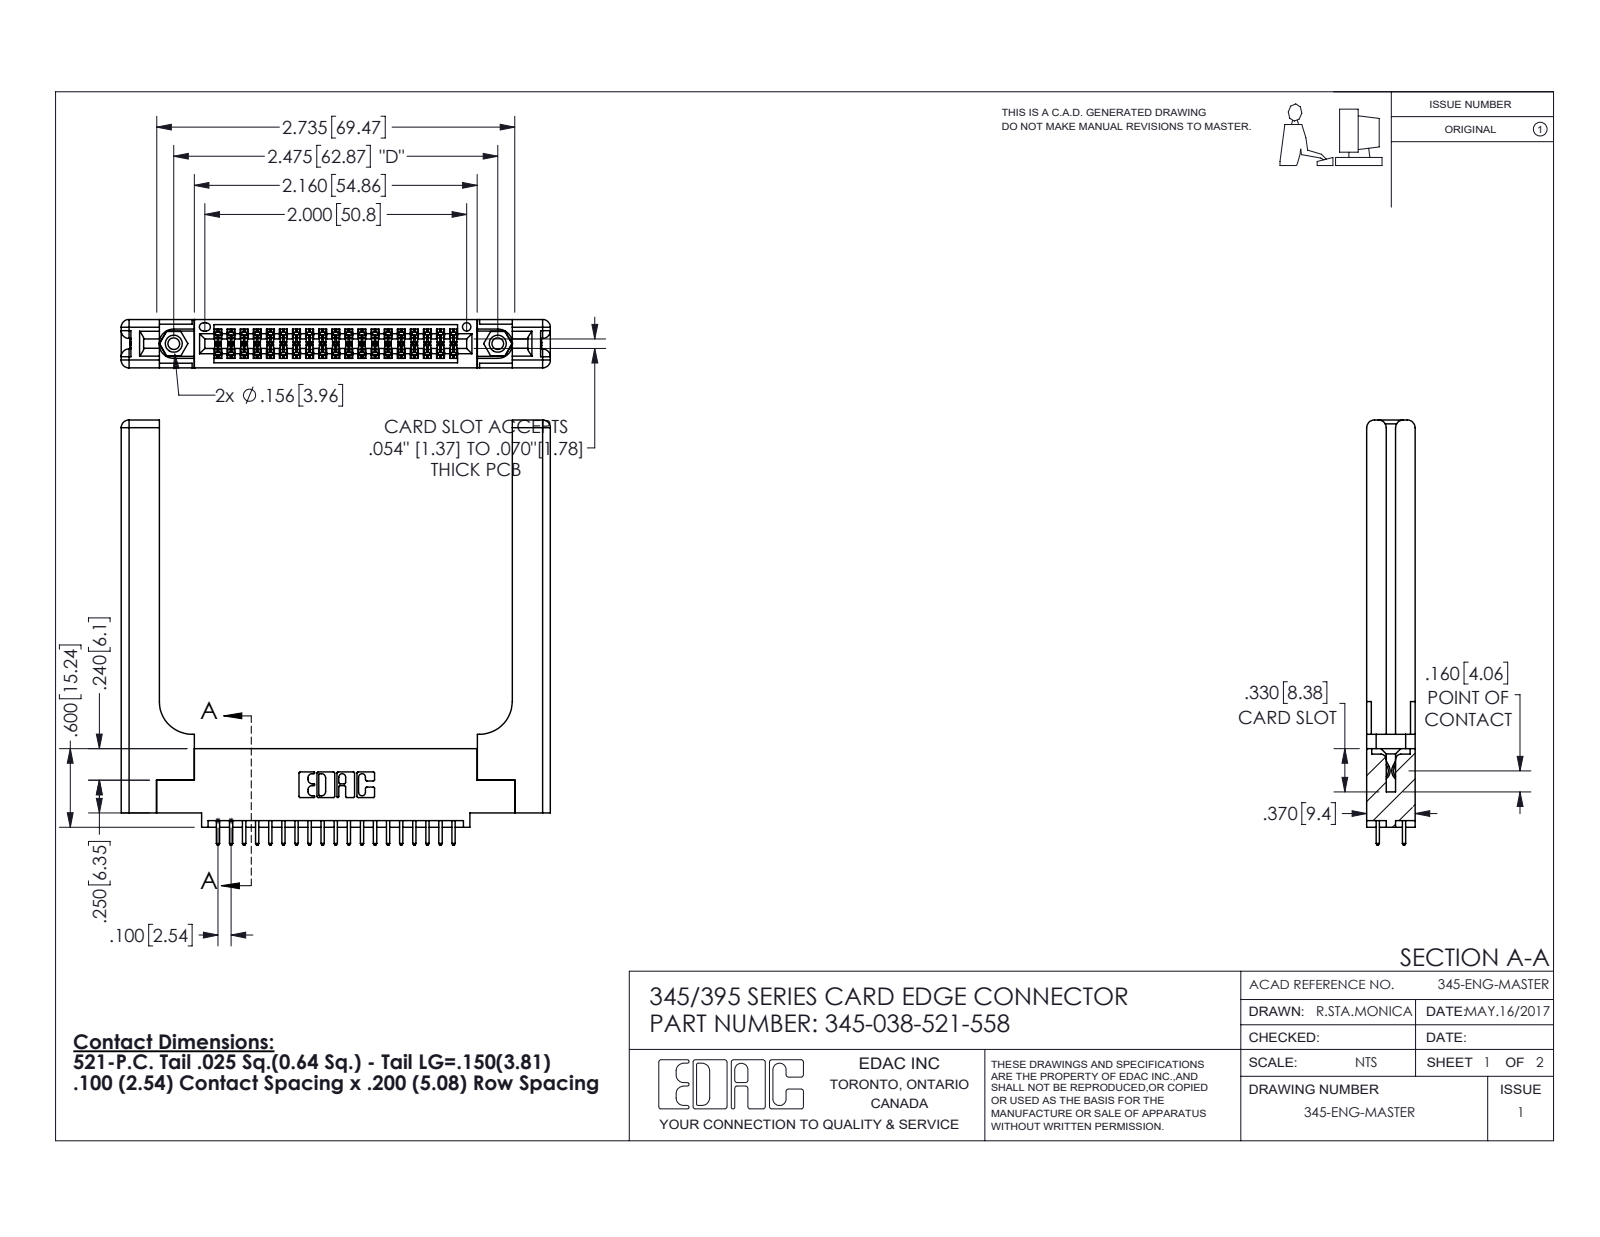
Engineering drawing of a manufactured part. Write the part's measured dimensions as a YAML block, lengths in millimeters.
part_name: "345-038-521-558; 345-250-001_345-250-001-102; 345-292-001_345-293-121; 345 Part_0.110 Offset - 0.156 Dia-TH (+1 more)"
step_written_by: "SolidWorks 2016 (CONFIG_CONTROL_DESIGN)"
units: millimeters
bodies: {solids: 43, faces: 2286, planar: 1486, cylindrical: 740, other: 60}
overall_size: [83.3, 82.5, 9.4]
volume: 16300
surface_area: 16120
round_holes:
  - {diameter: 2.3, count: 2}
  - {diameter: 3.2, count: 2}
  - {diameter: 4, count: 2}
  - {diameter: 1.6, count: 1}
round_bosses_or_shafts:
  - {diameter: 3.9, count: 2}
partial_cylinders:
  - {radius: 0.2, count: 57}
  - {radius: 0.3, count: 38}
  - {radius: 0.3, count: 22}
  - {radius: 1.5, count: 16}
  - {radius: 0.2, count: 6}
  - {radius: 0.8, count: 6}
  - {radius: 0.7, count: 3}
  - {radius: 0.4, count: 2}
face_to_face_distances: [9.4, 1.8, 7.6, 3.8, 3.8, 2, 5.1, 5.7, 2.5, 6.9]
hole_center_spacings: [6.9, 56.9, 62.9]
